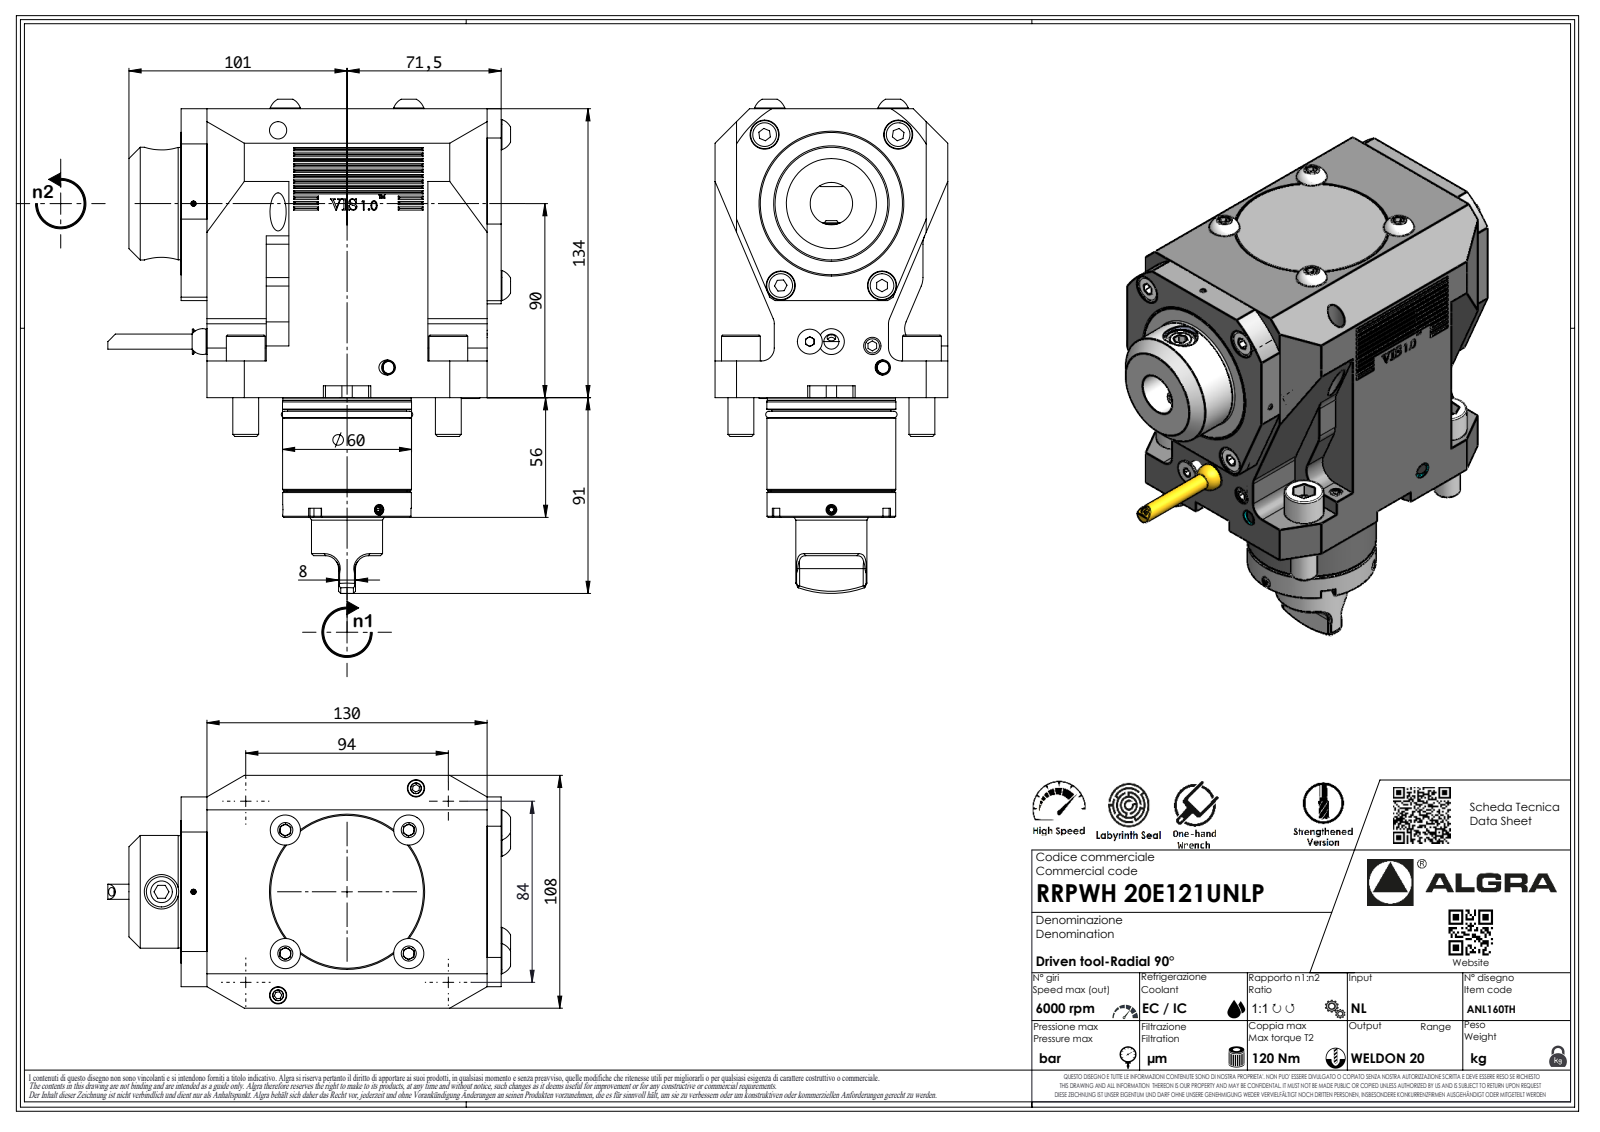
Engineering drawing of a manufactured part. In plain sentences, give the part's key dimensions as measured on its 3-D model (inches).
The part is named "RRPWH20E121UNLP". Its 3-D file was written by "SolidWorks 2023 (AUTOMOTIVE_DESIGN)". It is 1 solid with 919 faces: 635 planar, 112 cylindrical and 172 other. Overall it measures 8.85 by 7.185 by 4.252 inches. Its volume is 123.7 cubic inches and its surface area 194 square inches. Round holes: 1 of diameter 0.083, 1 of diameter 0.157. Round bosses or shafts: 4 of diameter 0.709, 4 of diameter 0.472, 1 of diameter 2.358, 1 of diameter 2.354, 1 of diameter 2.35, 1 of diameter 2.343, 1 of diameter 2.173, 1 of diameter 2.059. Partial cylindrical surfaces (rounded edges, fillets, slot ends): 21 of radius 0.008, 18 of radius 0.315, 10 of radius 0.236, 7 of radius 0.013, 7 of radius 0.02, 7 of radius 0.146, 4 of radius 0.394, 3 of radius 0.118. The main face-to-face distances are 5.276, 4.252, 1.083, 0.472, 4.035, 5.846, 0.256, 5.374, 0.217, 1.555.
